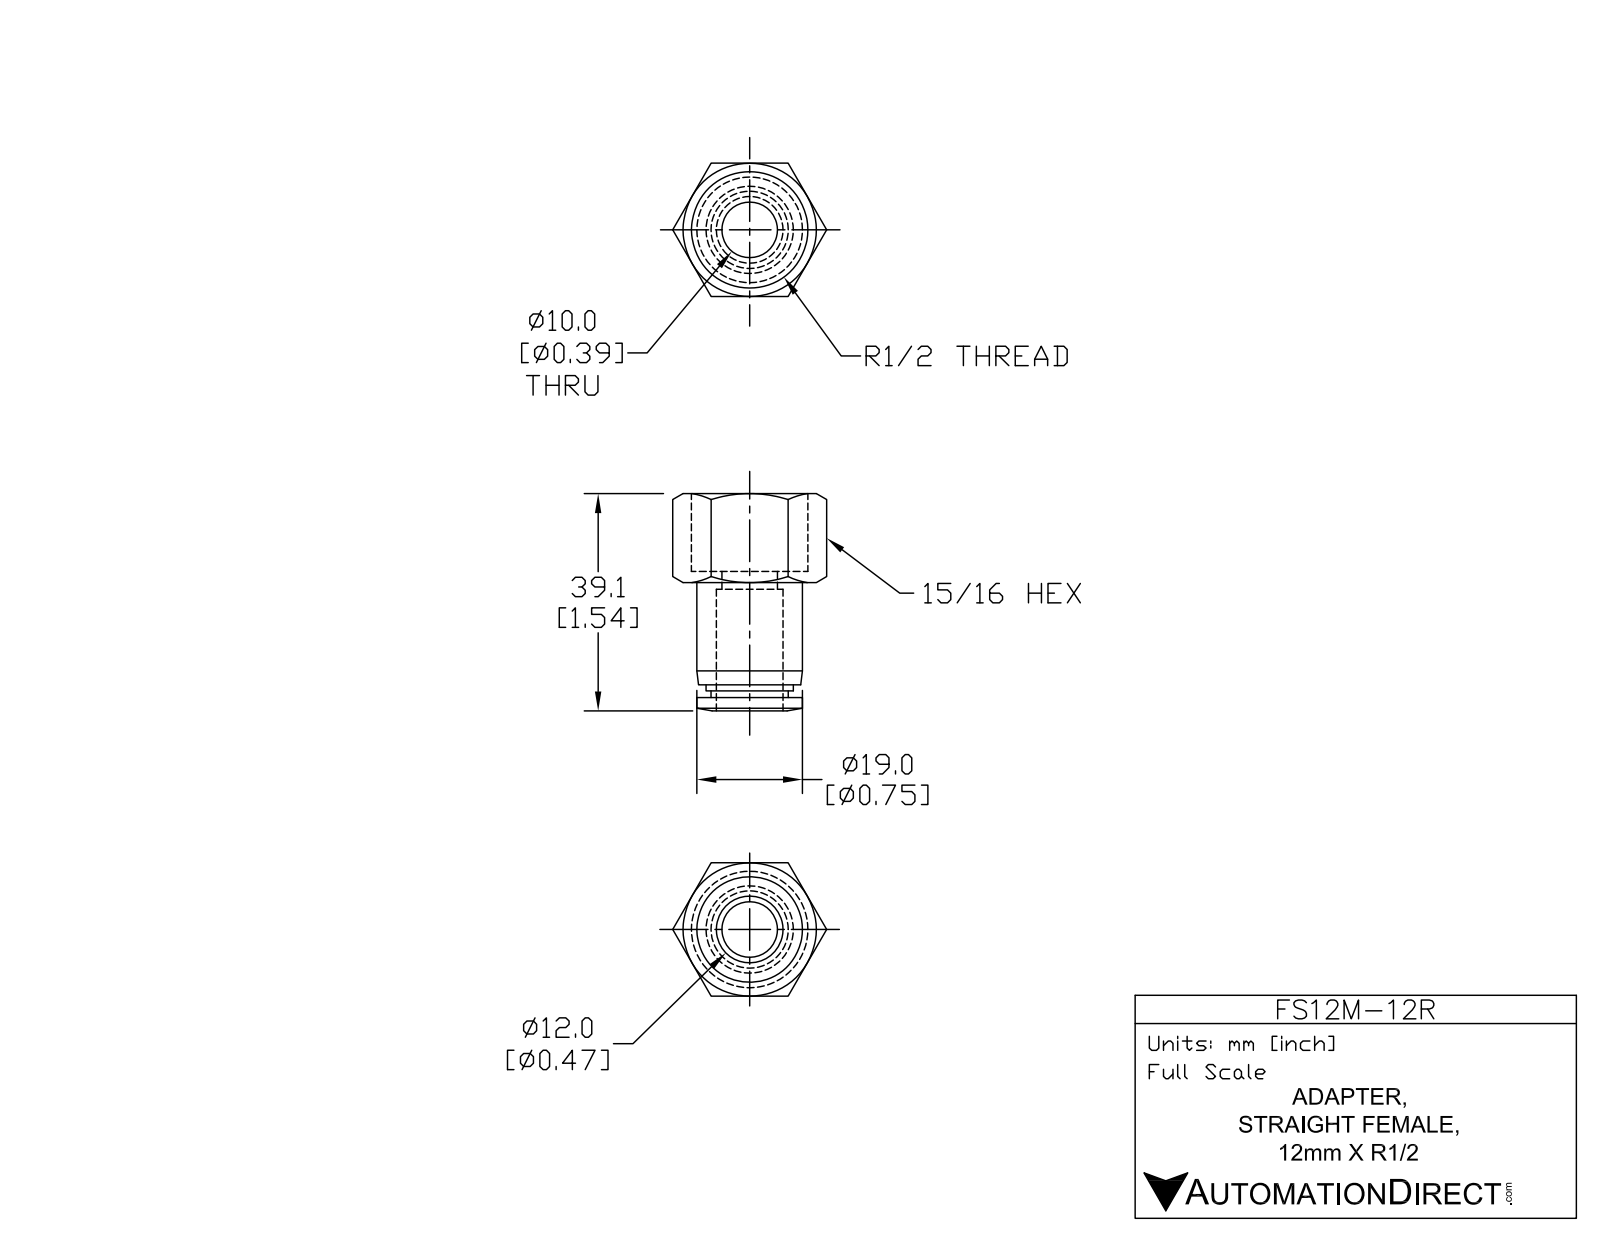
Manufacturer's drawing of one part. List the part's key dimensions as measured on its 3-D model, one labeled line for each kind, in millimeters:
Part name (STEP PRODUCT): FS12M-12R
STEP written by: SolidWorks 2015 (AUTOMOTIVE_DESIGN)
Units: millimetres
Bodies: 1 solid, 48 faces (14 planar, 12 cylindrical, 22 other)
Overall size (bounding box): 39.1 × 27.7 × 24
Volume: 6 700 mm³ · Surface area: 5 506 mm²
Round holes (diameter × count): ⌀10 ×1, ⌀12.3 ×1
Round bosses / shafts (diameter × count): ⌀19 ×1, ⌀15.7 ×1, ⌀13.9 ×1
Main face-to-face distances: 24, 2, 22.7, 20.7, 14, 16, 36.7, 1.2, 19.5, 17.2
